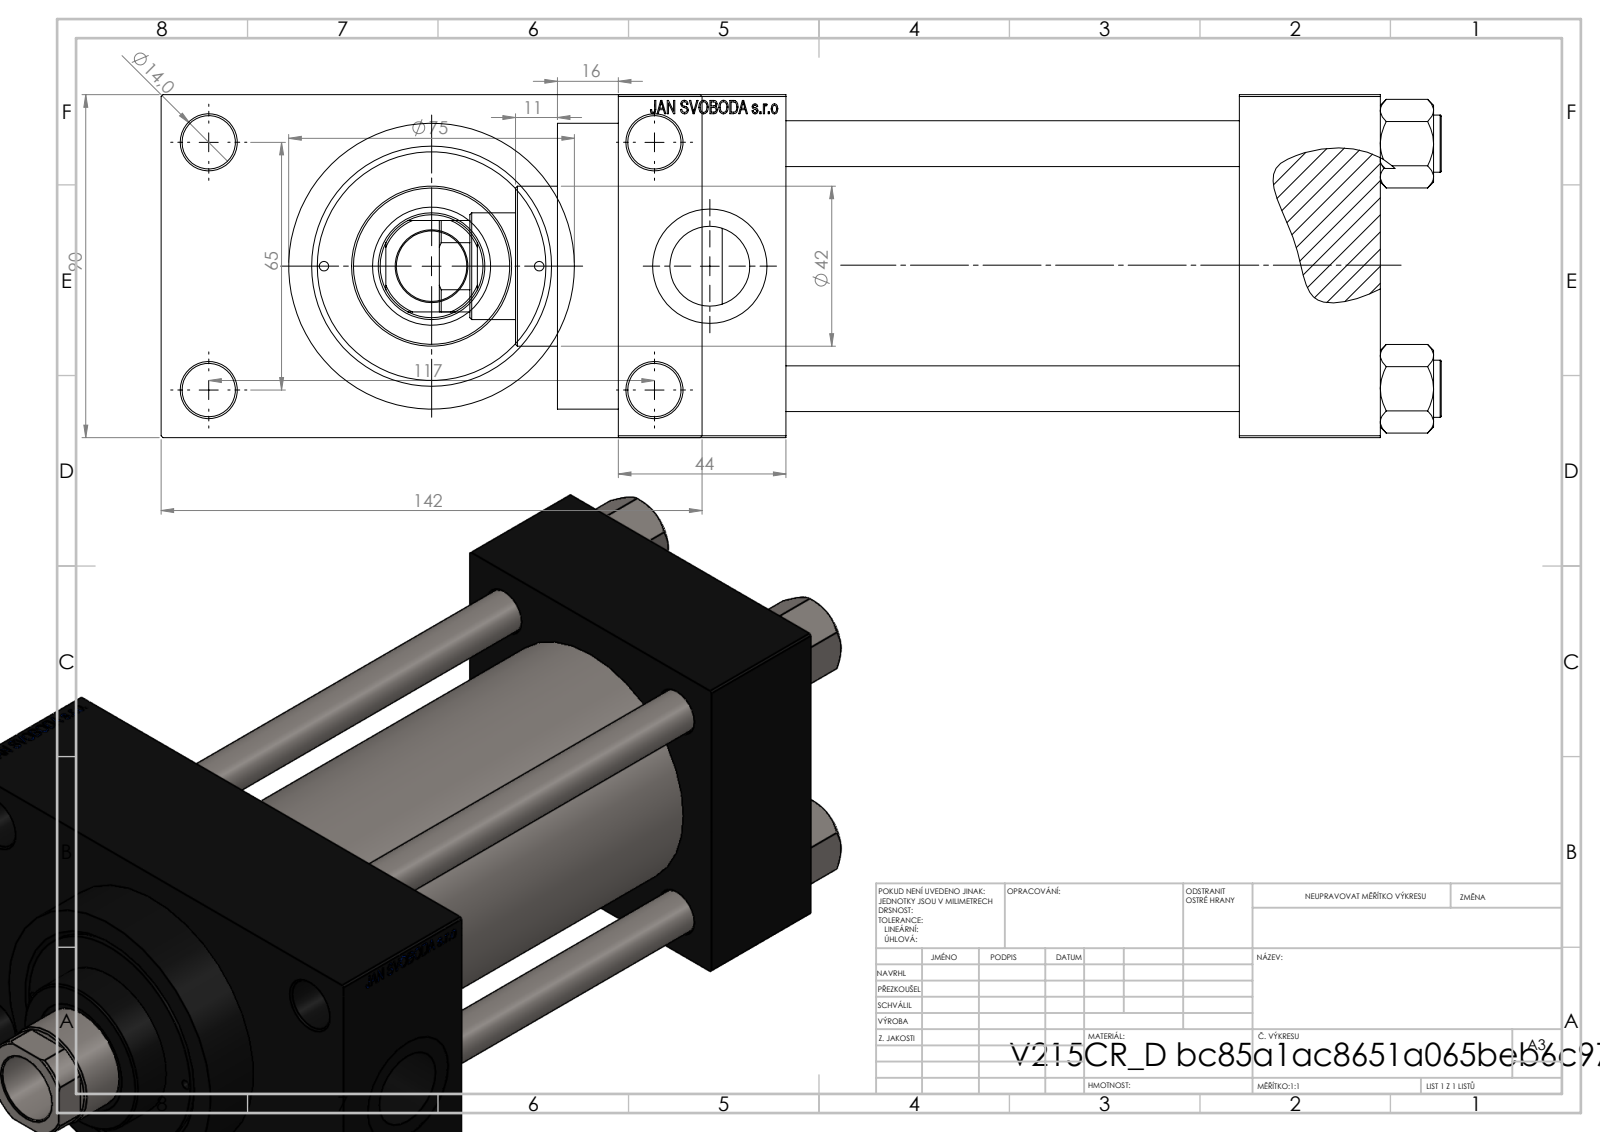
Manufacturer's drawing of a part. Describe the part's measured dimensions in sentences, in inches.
The part is named "V215_VC_A; V215CR_D_TYCINKA; V215CR_D_Body; V215CR_VCP_D (+1 more)". Its 3-D file was written by "SolidWorks 2019 (CONFIG_CONTROL_DESIGN)". It is 11 solids with 1111 faces: 499 planar, 92 cylindrical and 520 other. Overall it measures 10.354 by 5.591 by 3.543 inches. Its volume is 73.05 cubic inches and its surface area 371.1 square inches. Round holes: 4 of diameter 0.472, 4 of diameter 0.551, 2 of diameter 0.098, 2 of diameter 0.276, 2 of diameter 0.825, 2 of diameter 1.181, 1 of diameter 0.728, 1 of diameter 1.102, 1 of diameter 1.22, 1 of diameter 1.969, 1 of diameter 2.362, 1 of diameter 2.48. Round bosses or shafts: 4 of diameter 0.591, 1 of diameter 2.953, 1 of diameter 2.717, 1 of diameter 1.654. Partial cylindrical surfaces (rounded edges, fillets, slot ends): 1 of radius 0.531. The main face-to-face distances are 3.543, 4.685, 1.457, 6.142, 6.417, 7.874, 1.732, 4.567, 1.024, 0.63. The hole center spacings are 1.037, 1.275, 1.748, 1.79, 2.531, 2.635, 2.694, 2.748.
